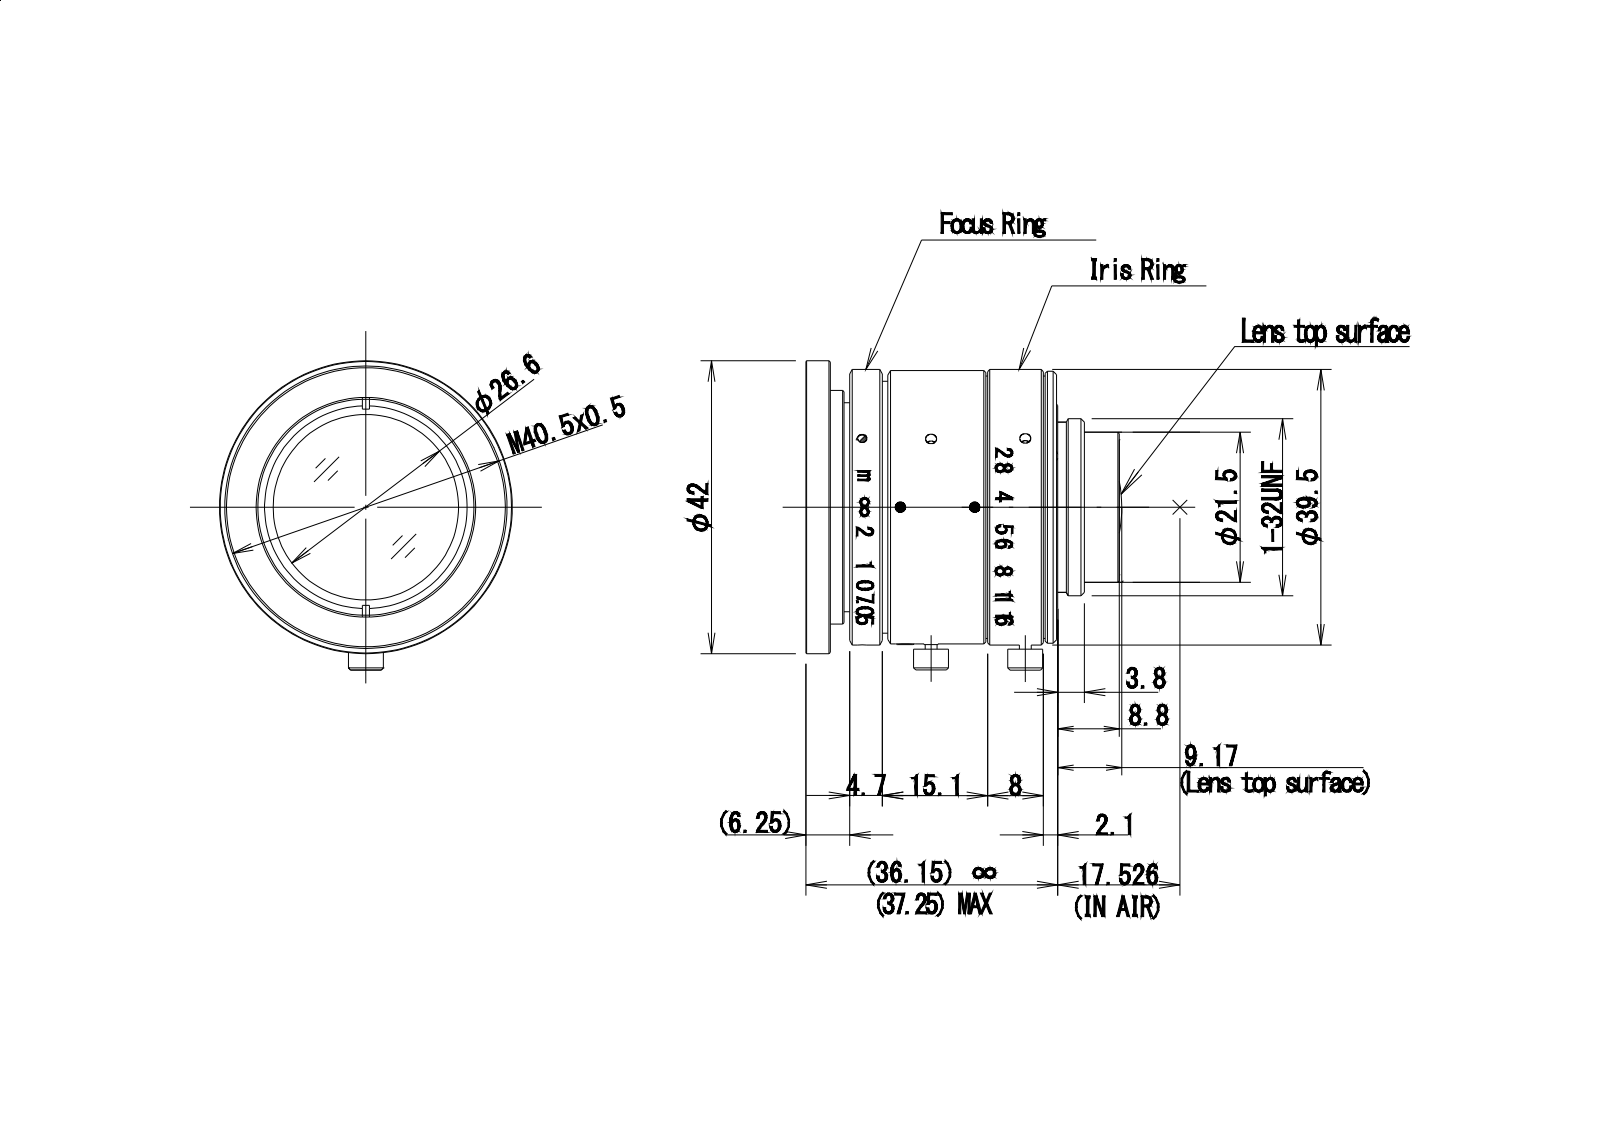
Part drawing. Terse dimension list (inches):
name: Reference 3D-drawing of V1228-MPY2_12mm
written by: ST-DEVELOPER v16.7 (AUTOMOTIVE_DESIGN)
unit: in
bodies: 1 solid, 278 faces (166 planar, 68 cylindrical, 44 other)
size: 1.828 × 1.746 × 1.654
volume: 2.674 in³; area: 16.15 in²
holes: 5× ⌀0.062, 3× ⌀0.052, 3× ⌀0.071, 3× ⌀0.138, 1× ⌀0.11, 1× ⌀0.118, 1× ⌀0.134, 1× ⌀0.661, 1× ⌀1.047, 1× ⌀1.575, 1× ⌀1.594
bosses: 6× ⌀0.067, 4× ⌀0.118, 2× ⌀0.197, 2× ⌀0.098, 1× ⌀1.654, 1× ⌀1.555, 1× ⌀1.543, 1× ⌀1.535
rounds: 1× R0.026, 1× R0.384, 1× R0.61, 1× R0.699, 1× R0.717
face distances: 0.039, 0.193, 0.154, 1.361, 1.322, 1.169, 1.368, 1.329, 1.175, 0.117
hole spacings: 0.642, 0.389, 0.532, 0.921, 1.111, 0.243, 1.112
